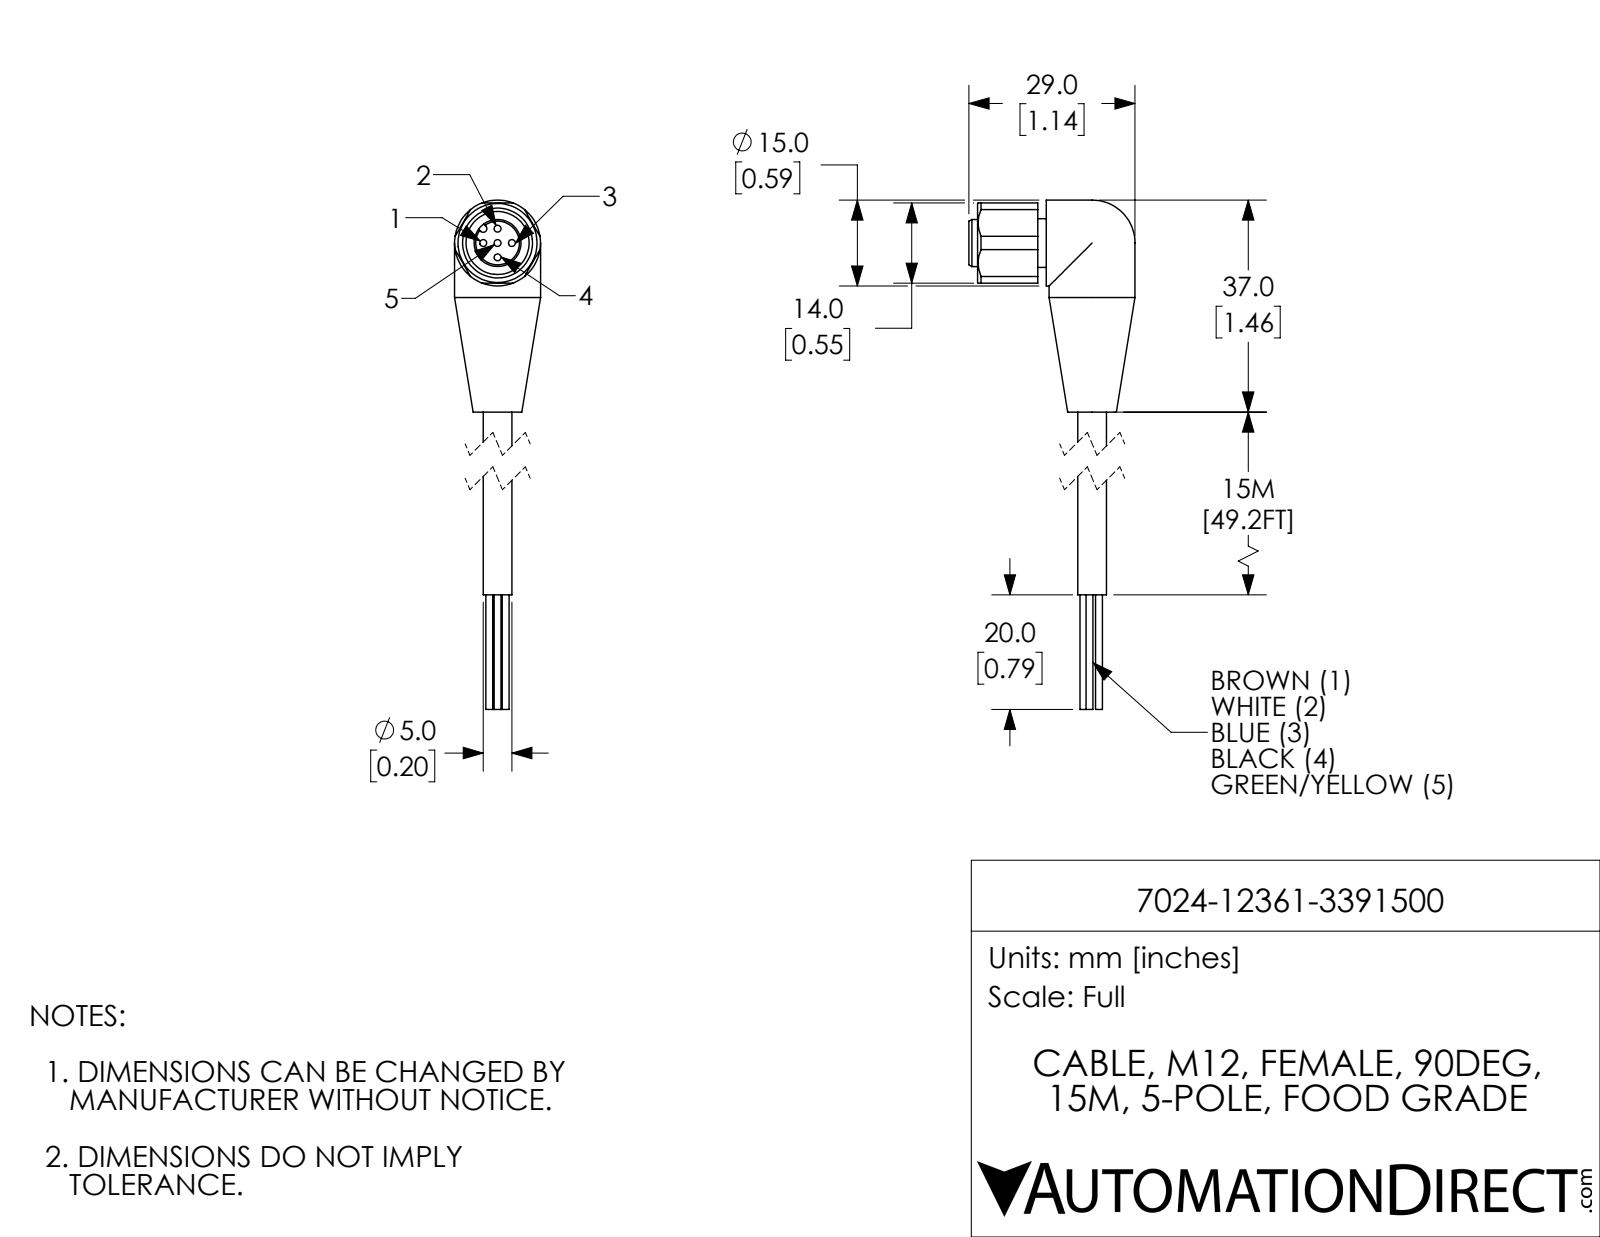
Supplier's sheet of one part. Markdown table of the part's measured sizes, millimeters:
| quantity | value |
| --- | --- |
| part name | 7024-12361-3391500 |
| STEP written by | SolidWorks 2018 (AUTOMOTIVE_DESIGN) |
| units | millimeters |
| bodies | 1 solid, 76 faces (26 planar, 40 cylindrical, 10 other) |
| overall size | 87 × 29 × 15 |
| volume | 7 424 mm³ |
| surface area | 3 961 mm² |
| round holes (diameter × count) | 1.2 × 5, 11 × 1 |
| round bosses / shafts (diameter × count) | 1.2 × 5, 15 × 2, 8.5 × 1, 8.2 × 1, 5 × 1 |
| partial cylindrical surfaces (radius × count) | 0.65 × 1 |
| main face-to-face distances | 14, 1.5, 12, 4.5, 3, 13.5, 9, 22.5, 36.5, 10.5 |
| hole center spacings | 2.5, 3.54, 5 |
